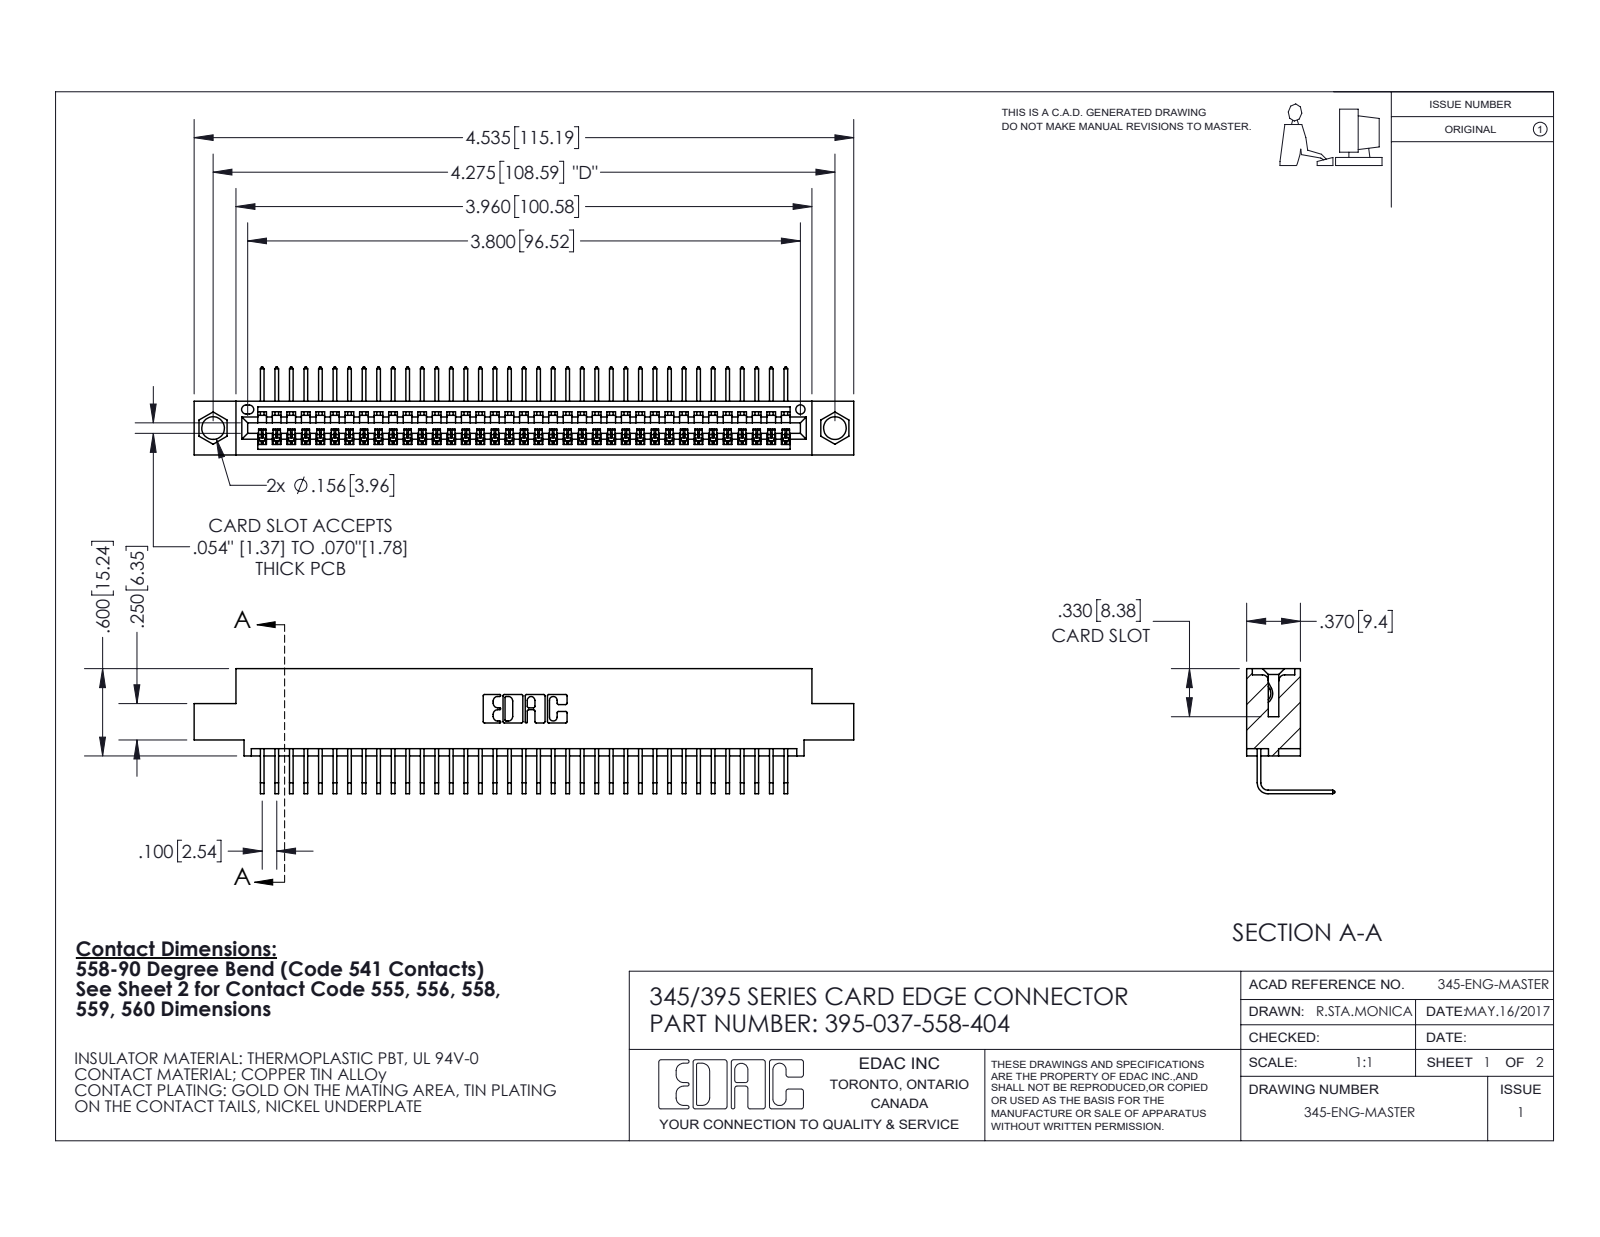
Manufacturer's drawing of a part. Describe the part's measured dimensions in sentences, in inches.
The part is named "345 Part_0.110 Offset - 0.156 Dia-TI; 395-037-558-404; 345-292-001_558 Tail - 2". Its 3-D file was written by "SolidWorks 2020 (CONFIG_CONTROL_DESIGN)". It is 38 solids with 2364 faces: 1652 planar, 712 cylindrical and 0 other. Overall it measures 4.535 by 0.859 by 0.605 inches. Its volume is 0.662 cubic inches and its surface area 23.24 square inches. Round holes: 2 of diameter 0.156, 1 of diameter 0.064. Partial cylindrical surfaces (rounded edges, fillets, slot ends): 74 of radius 0.006, 22 of radius 0.01, 6 of radius 0.007, 6 of radius 0.031, 3 of radius 0.026, 2 of radius 0.031, 2 of radius 0.04, 1 of radius 0.014. The main face-to-face distances are 0.072, 0.298, 0.37, 0.2, 0.098, 0.272, 0.025, 0.225, 0.149, 0.072. The hole center spacings are 0.27, 4.039, 4.275.
